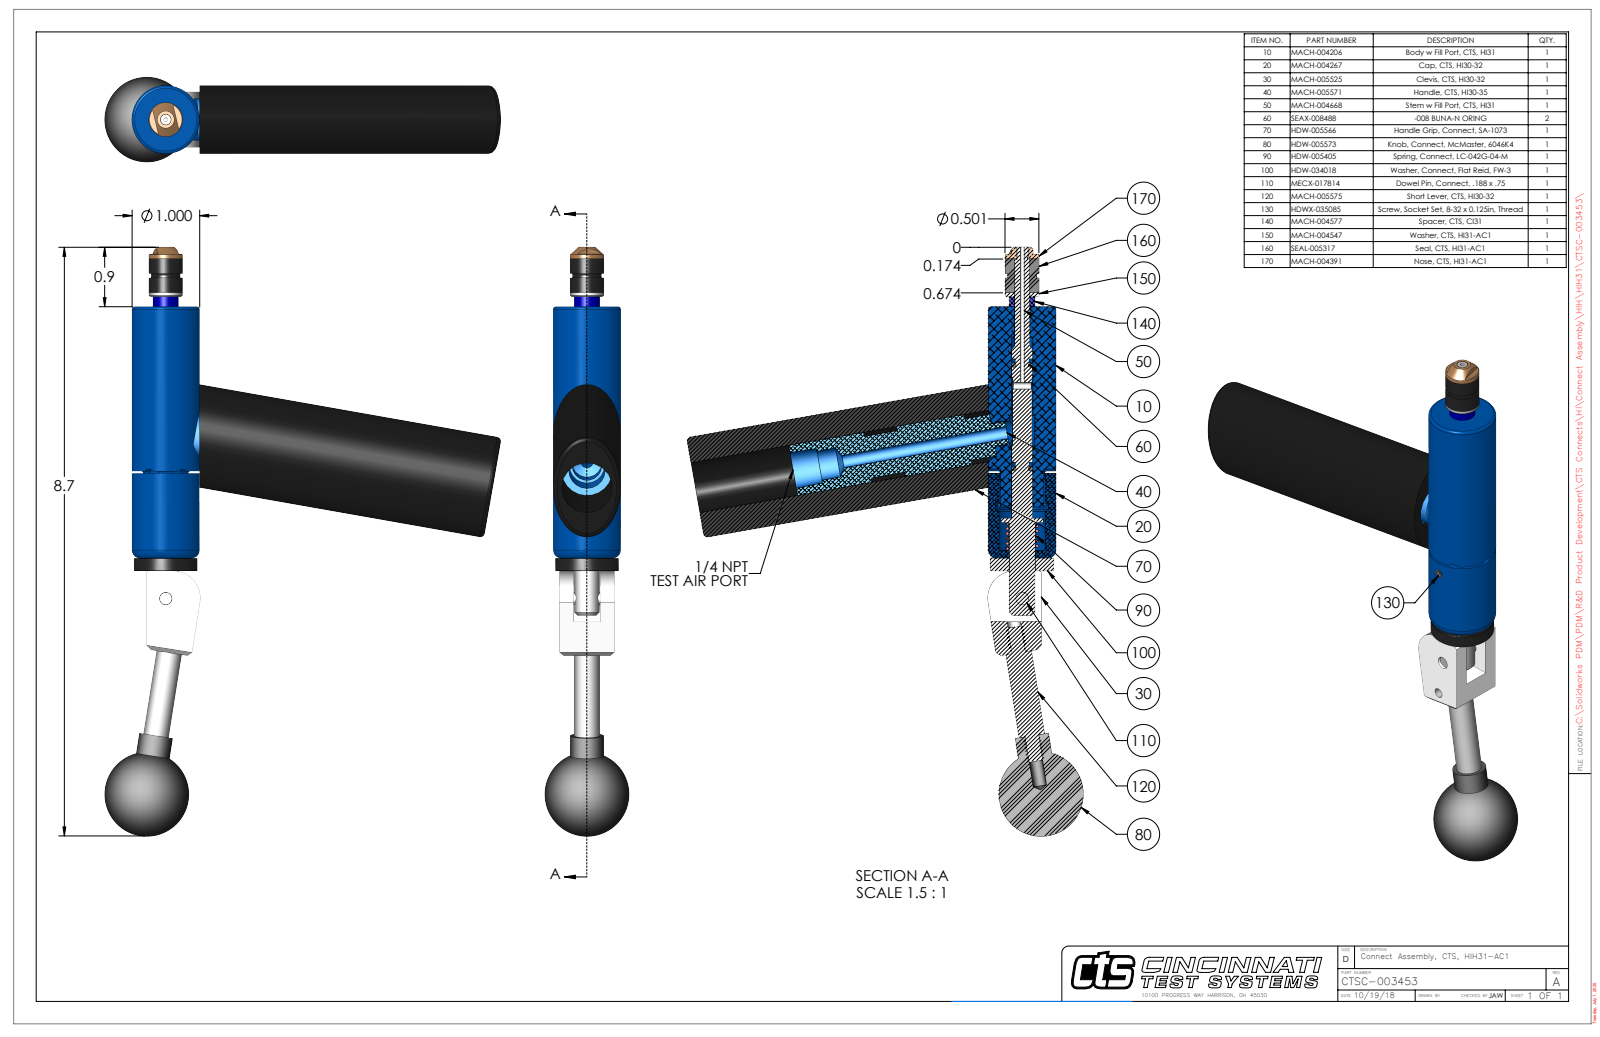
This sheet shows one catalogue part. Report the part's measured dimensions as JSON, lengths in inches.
{"part_name": "CTSC-003453", "step_written_by": "SolidWorks 2023 (AUTOMOTIVE_DESIGN)", "units": "inches", "bodies": {"solids": 11, "faces": 296, "planar": 102, "cylindrical": 126, "other": 68}, "overall_size": [8.704, 5.856, 1.25], "volume_in3": 9.202, "surface_area_in2": 74.82, "round_holes": [[0.201, 2], [0.063, 1], [0.109, 1], [0.111, 1], [0.136, 1], [0.15, 1], [0.159, 1], [0.187, 1], [0.189, 1], [0.218, 1], [0.228, 1], [0.229, 1]], "round_bosses_or_shafts": [[1, 1], [0.936, 1], [0.75, 1], [0.62, 1], [0.501, 1], [0.5, 1], [0.38, 1], [0.379, 1]], "partial_cylinders_radius": [[0.093, 6], [0.029, 2], [0.325, 1], [0.4, 1], [0.455, 1]], "face_to_face_distances": [0.21, 0.602, 0.812, 0.187, 3.716, 3.903, 0.785, 0.391, 2.463, 1.253], "hole_center_spacings": [0.599, 1.658, 2.252]}
